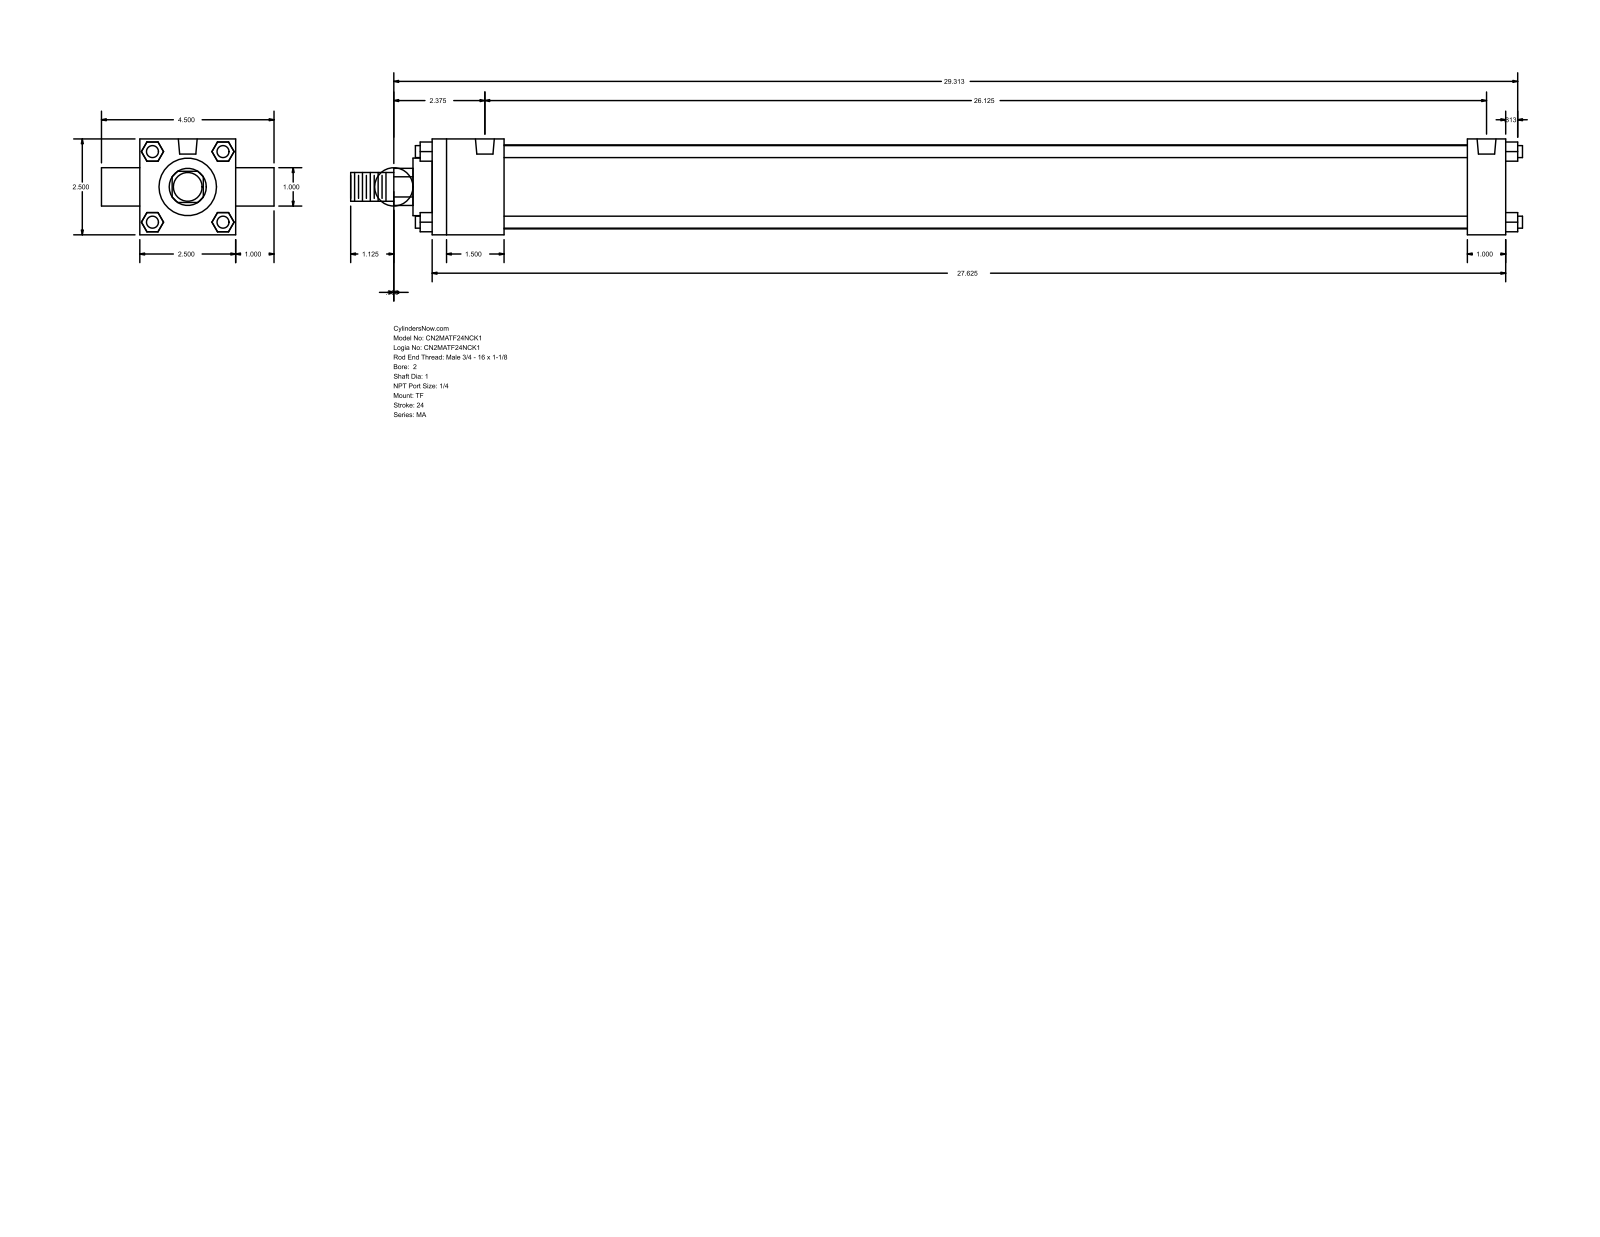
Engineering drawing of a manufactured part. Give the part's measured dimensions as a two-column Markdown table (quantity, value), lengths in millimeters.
| quantity | value |
| --- | --- |
| part name | MA_TF__0200_1 |
| STEP written by | GSSL Pune (CONFIG_CONTROL_DESIGN) |
| units | millimeters |
| bodies | 0 solids, 120 faces (92 planar, 28 cylindrical, 0 other) |
| overall size | 776.29 × 114.3 × 63.5 |
| round holes (diameter × count) | 7.94 × 3, 12.49 × 2 |
| round bosses / shafts (diameter × count) | 7.94 × 4, 25.4 × 2, 55.63 × 1, 38.1 × 1, 19.05 × 1 |
| partial cylindrical surfaces (radius × count) | 12.29 × 1 |
| main face-to-face distances | 63.5, 25.4, 711.2, 12.7, 47.63, 685.8, 638.17, 663.57, 88.9, 23.37 |
| hole center spacings | 663.57 |
